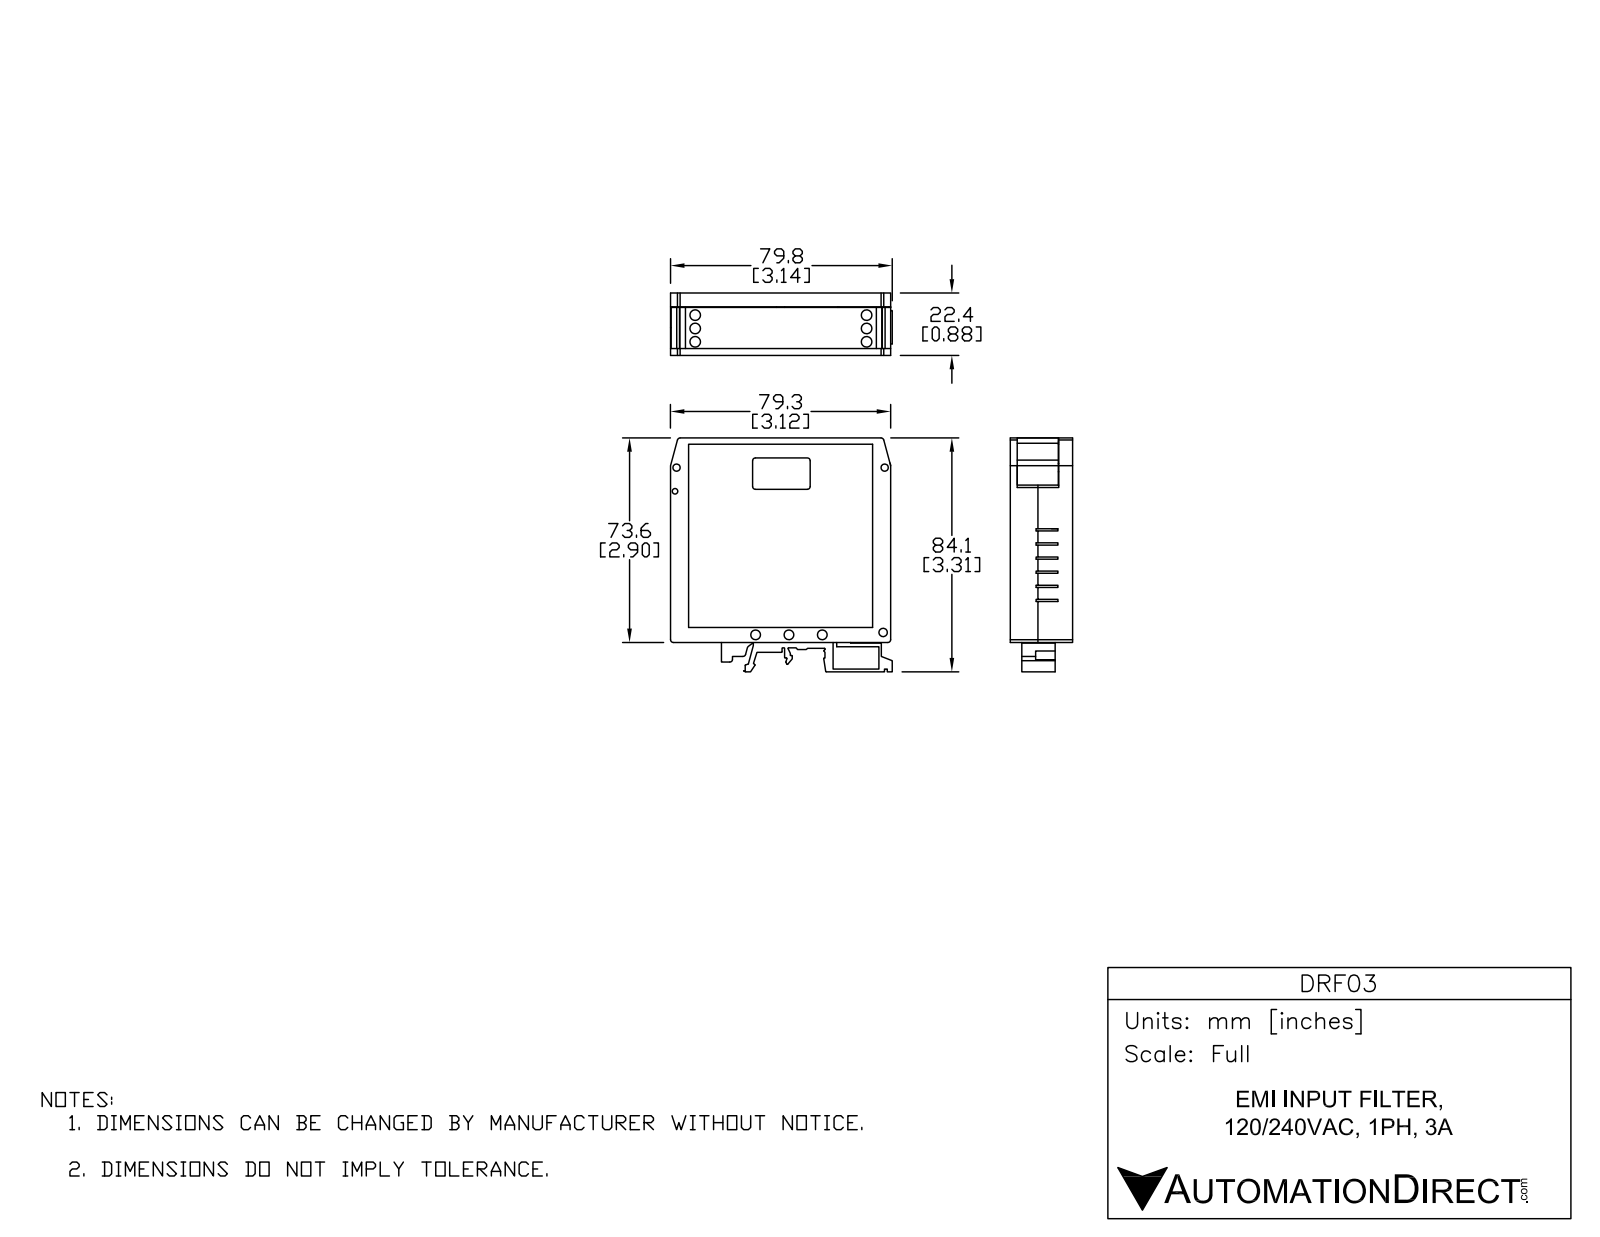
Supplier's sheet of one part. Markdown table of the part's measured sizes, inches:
| quantity | value |
| --- | --- |
| part name | DRF01-10 |
| STEP written by | SolidWorks 2017 (AUTOMOTIVE_DESIGN) |
| units | inches |
| bodies | 5 solids, 676 faces (463 planar, 169 cylindrical, 44 other) |
| overall size | 3.313 × 3.142 × 0.883 |
| volume | 2.485 in³ |
| surface area | 76.62 in² |
| round holes (diameter × count) | 0.138 × 6, 0.142 × 6, 0.15 × 6, 0.047 × 2, 0.079 × 2, 0.102 × 2, 0.118 × 2 |
| round bosses / shafts (diameter × count) | 0.118 × 2 |
| partial cylindrical surfaces (radius × count) | 0.008 × 17, 0.039 × 17, 0.016 × 8, 0.079 × 6, 0.118 × 2, 0.188 × 1, 0.191 × 1, 0.241 × 1 |
| main face-to-face distances | 0.051, 0.817, 0.765, 0.059, 0.868, 0.824, 0.876, 2.618, 0.883, 0.044 |
| hole center spacings | 0.236, 0.189, 0.472, 2.437, 0.709, 2.429, 2.992, 0.335 |
